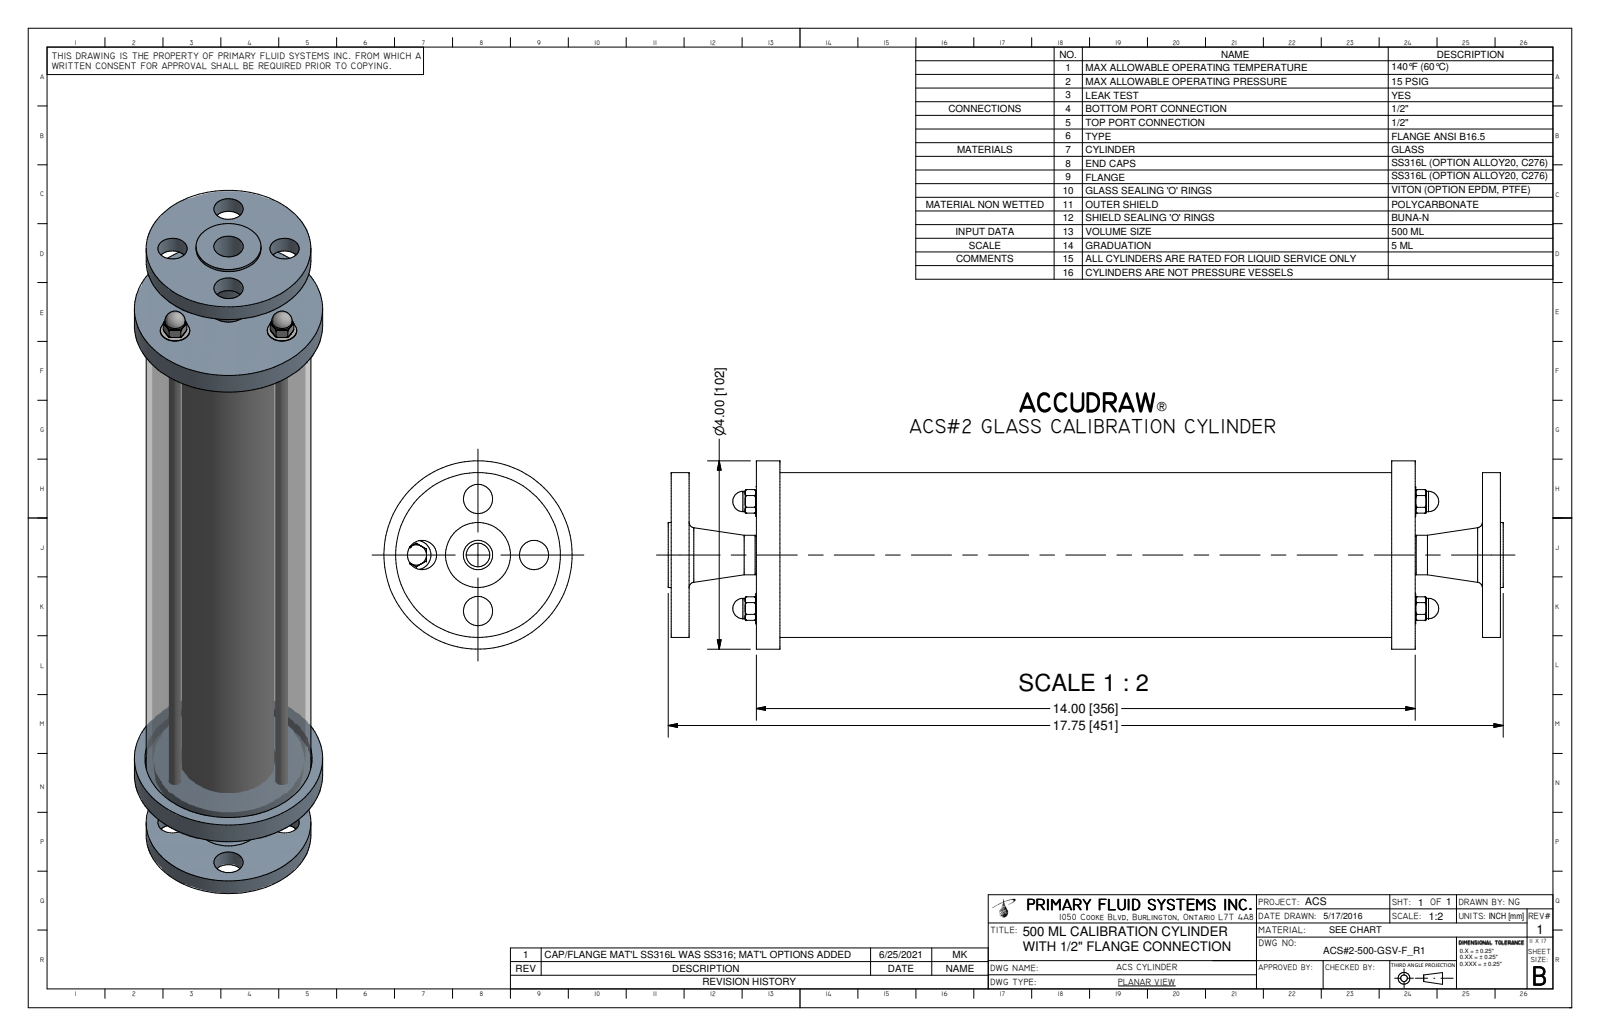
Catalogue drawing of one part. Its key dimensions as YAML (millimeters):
part_name: "ACS#2-500-GSV-F_R0; ACS-3-500-METAL-S_R1; ACS-2-500-PC_R6; ACS-1-500-A_R0 (+4 more)"
step_written_by: "Autodesk Inventor 2009 (AUTOMOTIVE_DESIGN)"
units: millimeters
bodies: {solids: 21, faces: 455, planar: 46, cylindrical: 57, other: 352}
overall_size: [450.7, 101.6, 101.6]
volume: 725100
surface_area: 409400
round_holes:
  - {diameter: 15.7, count: 4}
  - {diameter: 4.6, count: 3}
  - {diameter: 6.8, count: 3}
  - {diameter: 7.1, count: 3}
  - {diameter: 15.8, count: 1}
  - {diameter: 46, count: 1}
  - {diameter: 52.1, count: 1}
  - {diameter: 82.6, count: 1}
  - {diameter: 90.2, count: 1}
round_bosses_or_shafts:
  - {diameter: 15.9, count: 3}
  - {diameter: 6.4, count: 3}
  - {diameter: 101.6, count: 1}
  - {diameter: 88.9, count: 1}
  - {diameter: 81.3, count: 1}
  - {diameter: 50, count: 1}
  - {diameter: 43.2, count: 1}
  - {diameter: 35.1, count: 1}
face_to_face_distances: [12.7, 342.9, 46, 58.7, 388.9, 401.6, 9.7, 437.9, 36.3, 49]
hole_center_spacings: [30.2, 42.7, 33.4, 57.7, 16.7, 31.9, 45, 55.1]
